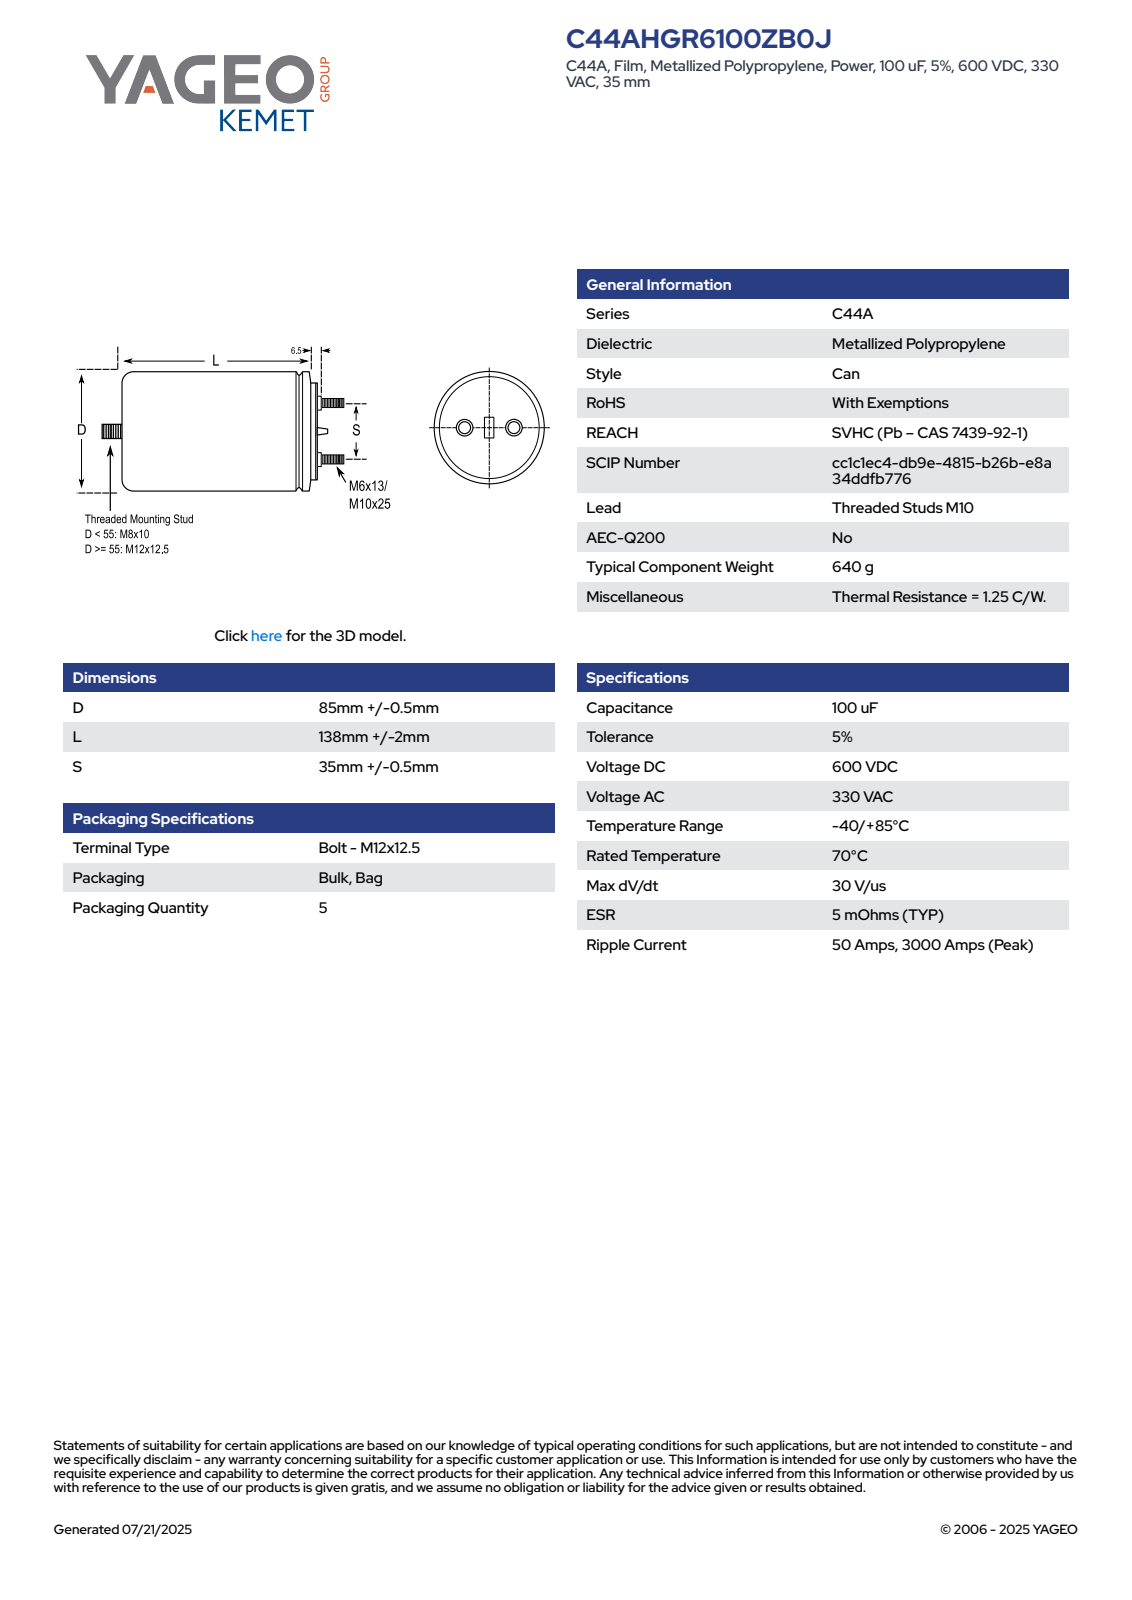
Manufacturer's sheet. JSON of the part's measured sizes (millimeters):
{"part_name": "CFP_C44A_85X138_D85.5L140S35", "step_written_by": "SolidWorks 2014 (AUTOMOTIVE_DESIGN)", "units": "millimeters", "bodies": {"solids": 1, "faces": 102, "planar": 29, "cylindrical": 34, "other": 39}, "overall_size": [172, 85.5, 85.5], "volume_mm3": 817709, "surface_area_mm2": 50921, "round_bosses_or_shafts": [[9, 2], [6, 2], [85.5, 1], [67.06, 1], [12, 1]], "partial_cylinders_radius": [[42.74, 1]], "face_to_face_distances": [145, 12.5, 157.5, 159, 146.5, 1.5, 172, 159.5, 14.5, 13]}
